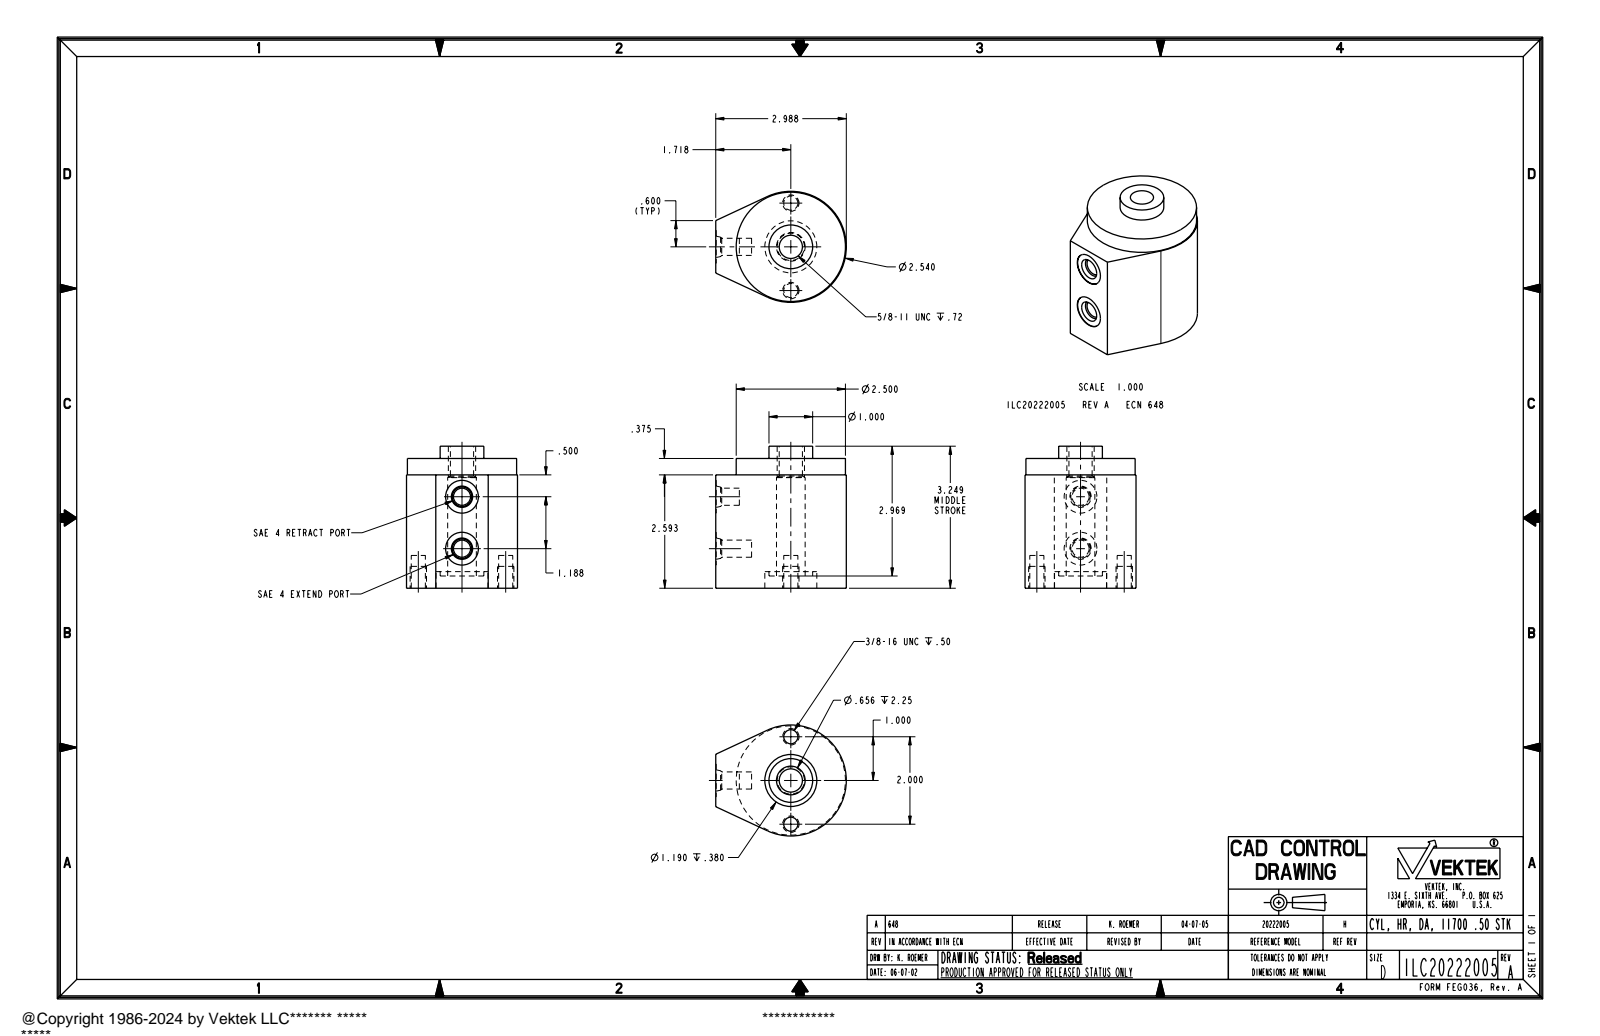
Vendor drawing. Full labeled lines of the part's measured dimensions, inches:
Part name (STEP PRODUCT): ILC20222005
STEP written by: PRO/ENGINEER BY PARAMETRIC TECHNOLOGY CORPORATION, 2004290 (AUTOMOTIVE_DESIGN_CC2)
Units: inches
Bodies: 1 solid, 58 faces (17 planar, 31 cylindrical, 10 other)
Overall size (bounding box): 3.249 × 2.988 × 2.54
Volume: 15.85 in³ · Surface area: 51.65 in²
Round holes (diameter × count): ⌀0.323 ×2, ⌀0.392 ×2, ⌀0.75 ×2, ⌀0.531 ×1, ⌀0.656 ×1, ⌀1.19 ×1
Round bosses / shafts (diameter × count): ⌀0.375 ×2, ⌀2.5 ×1, ⌀1 ×1, ⌀0.625 ×1
Partial cylindrical surfaces — rounded edges, fillets, slot ends (radius × count): R1.27 ×1
Main face-to-face distances: 2.968, 2.593, 0.375, 0.28, 3.249, 0.656, 0.281, 2.313, 2.688, 2.969
Hole centre spacings: 1, 1.188, 2
